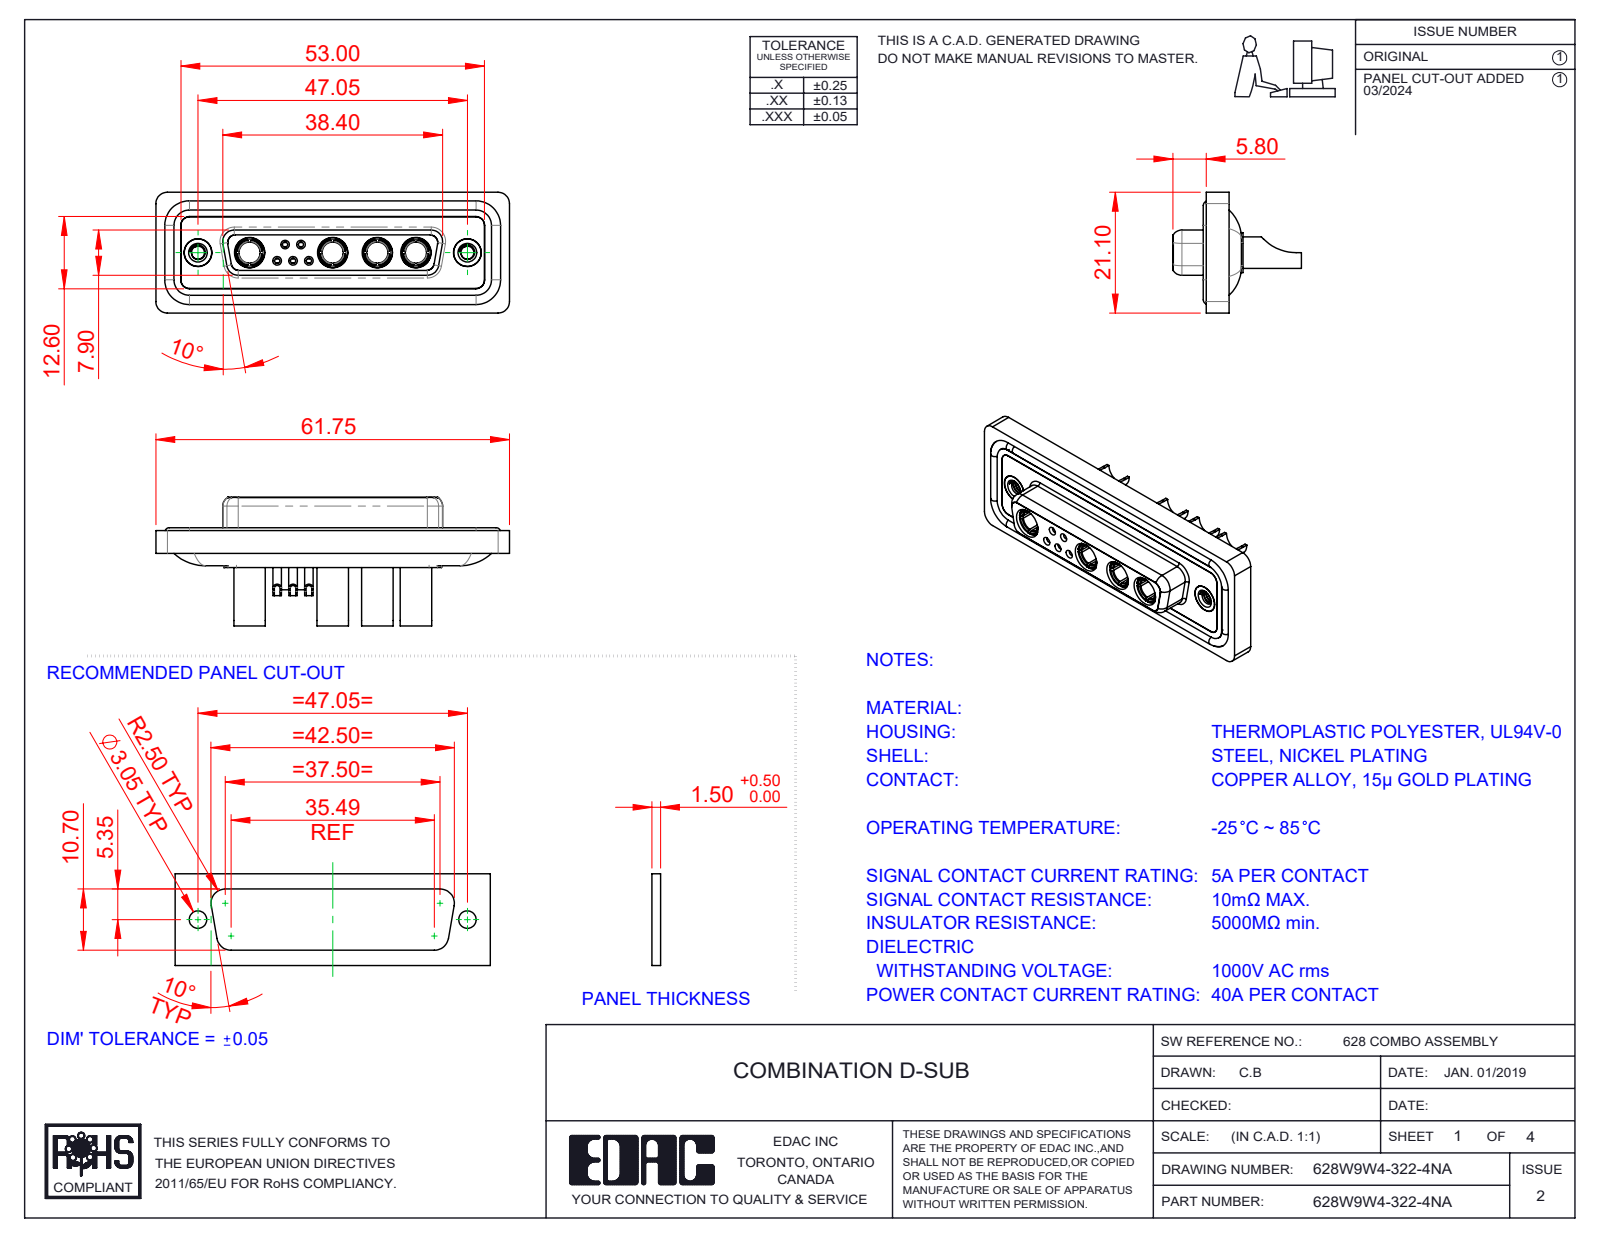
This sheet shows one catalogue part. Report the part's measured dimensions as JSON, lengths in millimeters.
{"part_name": "628Combo Shell Rear_25 Contacts; 628Combo Threaded Rivet_A; 628Combo Contact Row 1_22; 628Combo Shell Front_25 Contacts (+5 more)", "step_written_by": "SolidWorks 2023 (CONFIG_CONTROL_DESIGN)", "units": "millimeters", "bodies": {"solids": 20, "faces": 967, "planar": 314, "cylindrical": 391, "other": 262}, "overall_size": [61.75, 22.45, 21.1], "volume_mm3": 8396, "surface_area_mm2": 14174, "round_holes": [[4.85, 6], [0.9, 5], [1, 5], [1.1, 5], [1.5, 5], [2, 5], [3.7, 4], [4.6, 4], [5.3, 4], [1.6, 3], [1.7, 2], [2.26, 2]], "round_bosses_or_shafts": [[1.6, 6], [2.2, 5], [5.5, 4], [5.2, 4], [4.96, 4], [4.75, 4], [3.75, 4], [4.95, 2]], "partial_cylinders_radius": [[1.5, 22], [2, 18], [1.35, 8], [1.6, 8], [1, 6], [0.25, 4], [0.5, 4], [0.6, 4]], "face_to_face_distances": [0.4, 7.45, 1.8, 5.65, 0.5, 7.05, 6.6, 1.6, 1.1, 2.9], "hole_center_spacings": [3.16, 2.77, 5.03, 2.76, 4.4, 5.02, 5.54, 5.73]}
